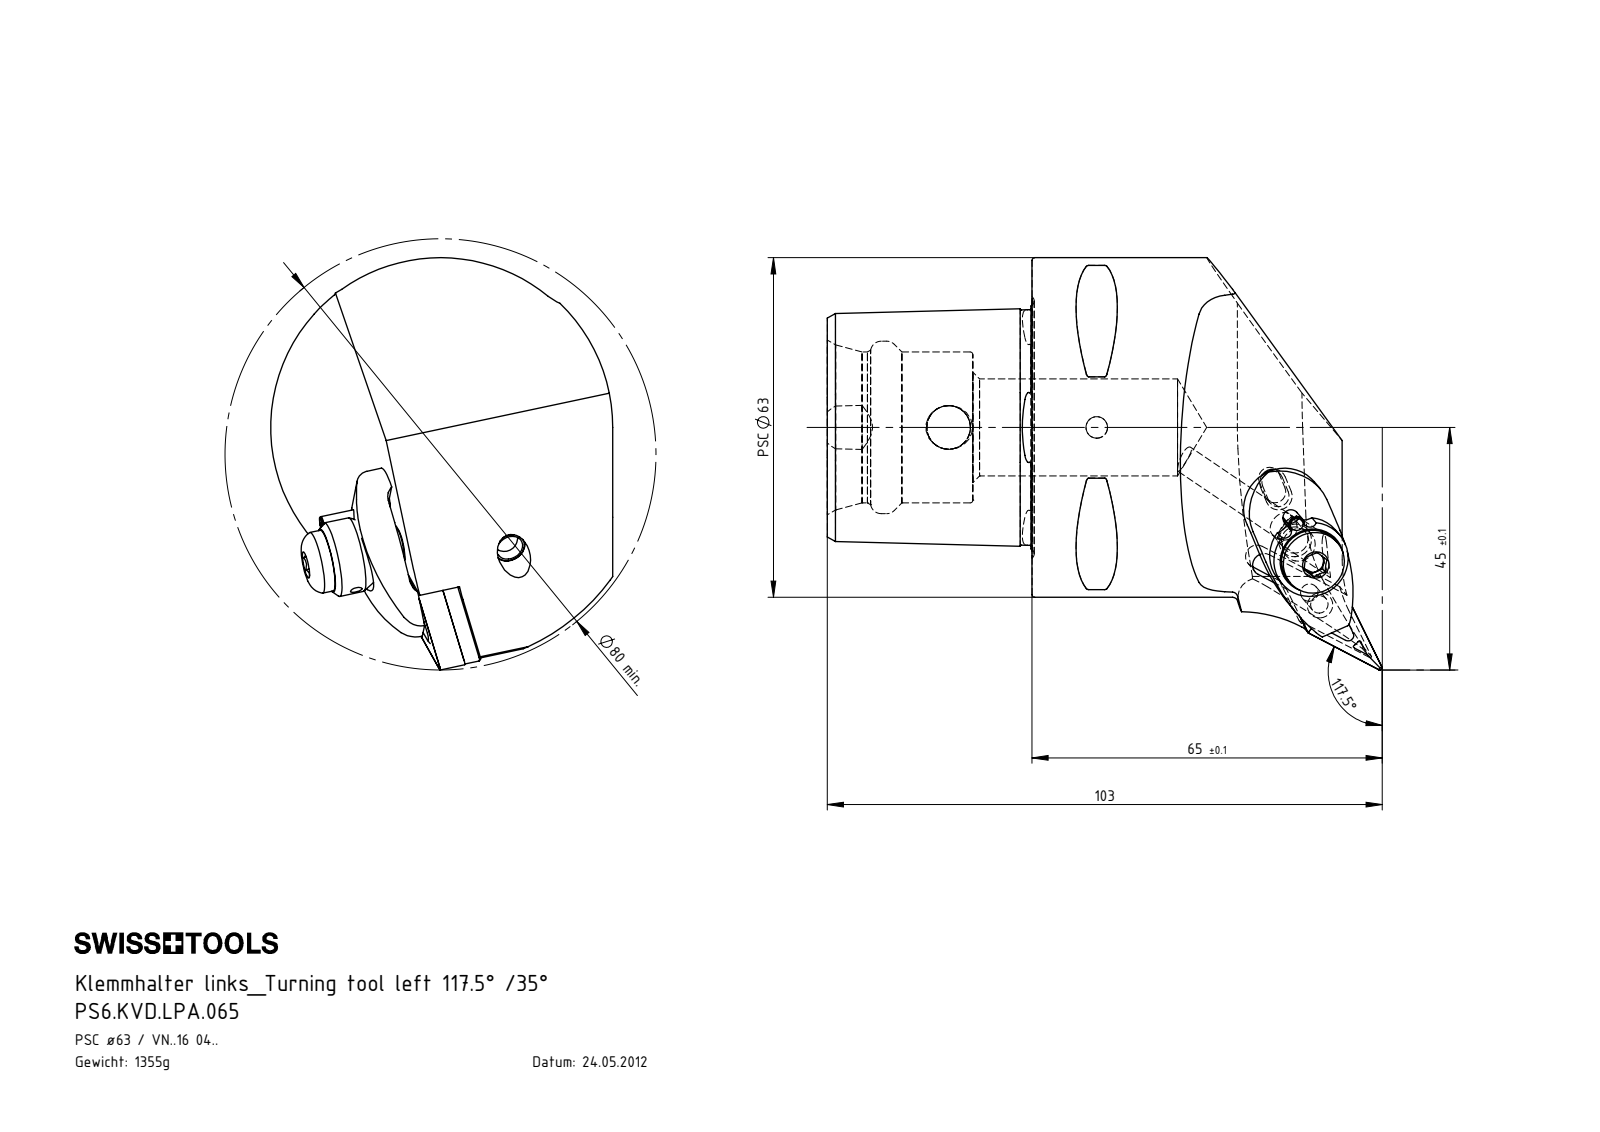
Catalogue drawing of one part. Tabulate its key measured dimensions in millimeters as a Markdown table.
| quantity | value |
| --- | --- |
| part name | PS6-KVD.LPA.065; KVT_MB_600_060; ISO 13337 - 3 x 12_PreviewCfg; WCC-ER4.103.032_A (+7 more) |
| STEP written by | SolidWorks 2012 (CONFIG_CONTROL_DESIGN) |
| units | millimeters |
| bodies | 11 solids, 430 faces (99 planar, 131 cylindrical, 200 other) |
| overall size | 103 × 76.5 × 63.5 |
| volume | 172 104 mm³ |
| surface area | 32 889 mm² |
| round holes (diameter × count) | 2 × 3, 5 × 3, 7 × 2, 2.4 × 1, 3 × 1, 3.3 × 1, 3.8 × 1, 4 × 1, 4.95 × 1, 6 × 1, 6.2 × 1, 6.9 × 1 |
| round bosses / shafts (diameter × count) | 6 × 2, 4 × 2, 3 × 2, 63 × 1, 14 × 1, 11.5 × 1, 6.8 × 1, 6.2 × 1 |
| partial cylindrical surfaces (radius × count) | 0.5 × 10, 0.34 × 6, 0.59 × 6, 0.4 × 4, 1.5 × 3, 6 × 3, 2 × 2, 3 × 2 |
| main face-to-face distances | 38, 24.88, 4.44, 27, 11, 9.11, 5.76, 1.32, 7.62, 55.8 |
| hole center spacings | 7.21, 7.22, 8.19, 21.52, 0.97, 0.98, 13.33, 14.3 |
